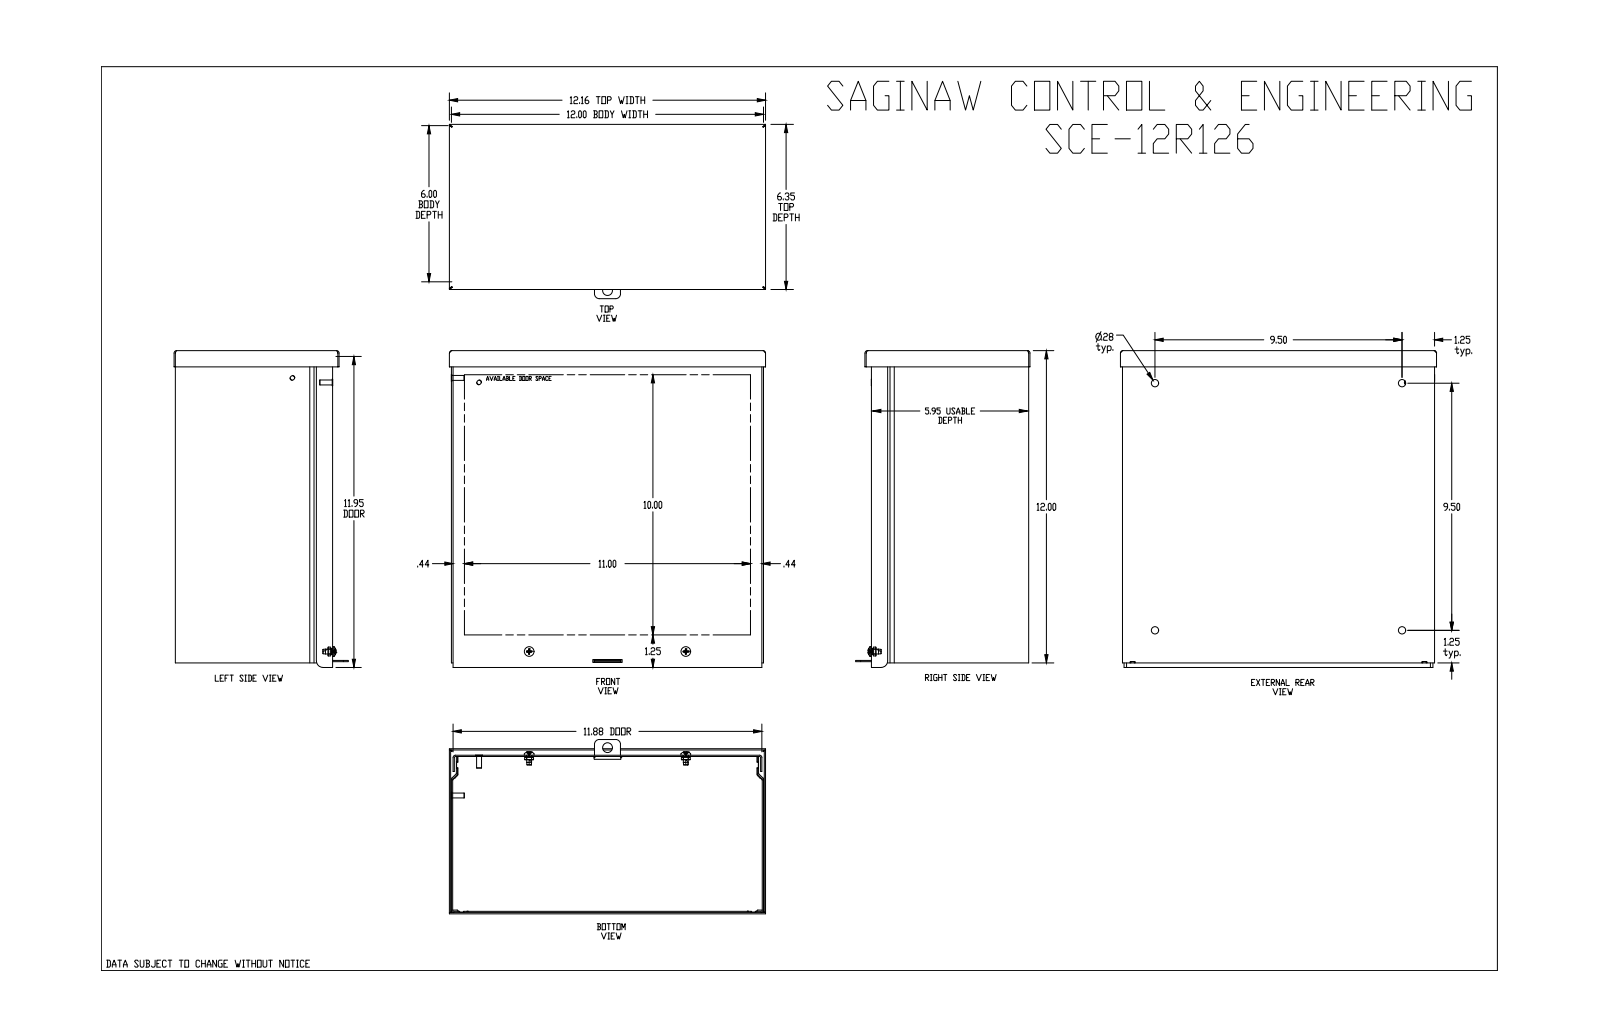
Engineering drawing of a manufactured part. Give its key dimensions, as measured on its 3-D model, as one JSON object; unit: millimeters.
{"part_name": "SCE-12R126", "step_written_by": "SolidWorks 2019 (AUTOMOTIVE_DESIGN)", "units": "millimeters", "bodies": {"solids": 11, "faces": 398, "planar": 181, "cylindrical": 143, "other": 74}, "overall_size": [309.2, 308.8, 170.1], "volume_mm3": 521800, "surface_area_mm2": 831600, "round_holes": [[7.1, 4], [4.8, 3], [6.4, 2], [4.8, 1], [4.9, 1], [9.5, 1]], "round_bosses_or_shafts": [[4.8, 4], [9.5, 2], [8.6, 2], [6.5, 2], [6.3, 2]], "partial_cylinders_radius": [[0.4, 32], [3.2, 12], [1.2, 8], [1.5, 8], [2.4, 8], [1.6, 6], [0.6, 4], [1.9, 4]], "face_to_face_distances": [1.2, 152.4, 303.6, 153.6, 151.2, 304.8, 1.5, 302.4, 302.1, 303.3], "hole_center_spacings": [241.3, 48.7, 198.2, 265.6, 327.8, 341.2, 4.8, 33.9]}
